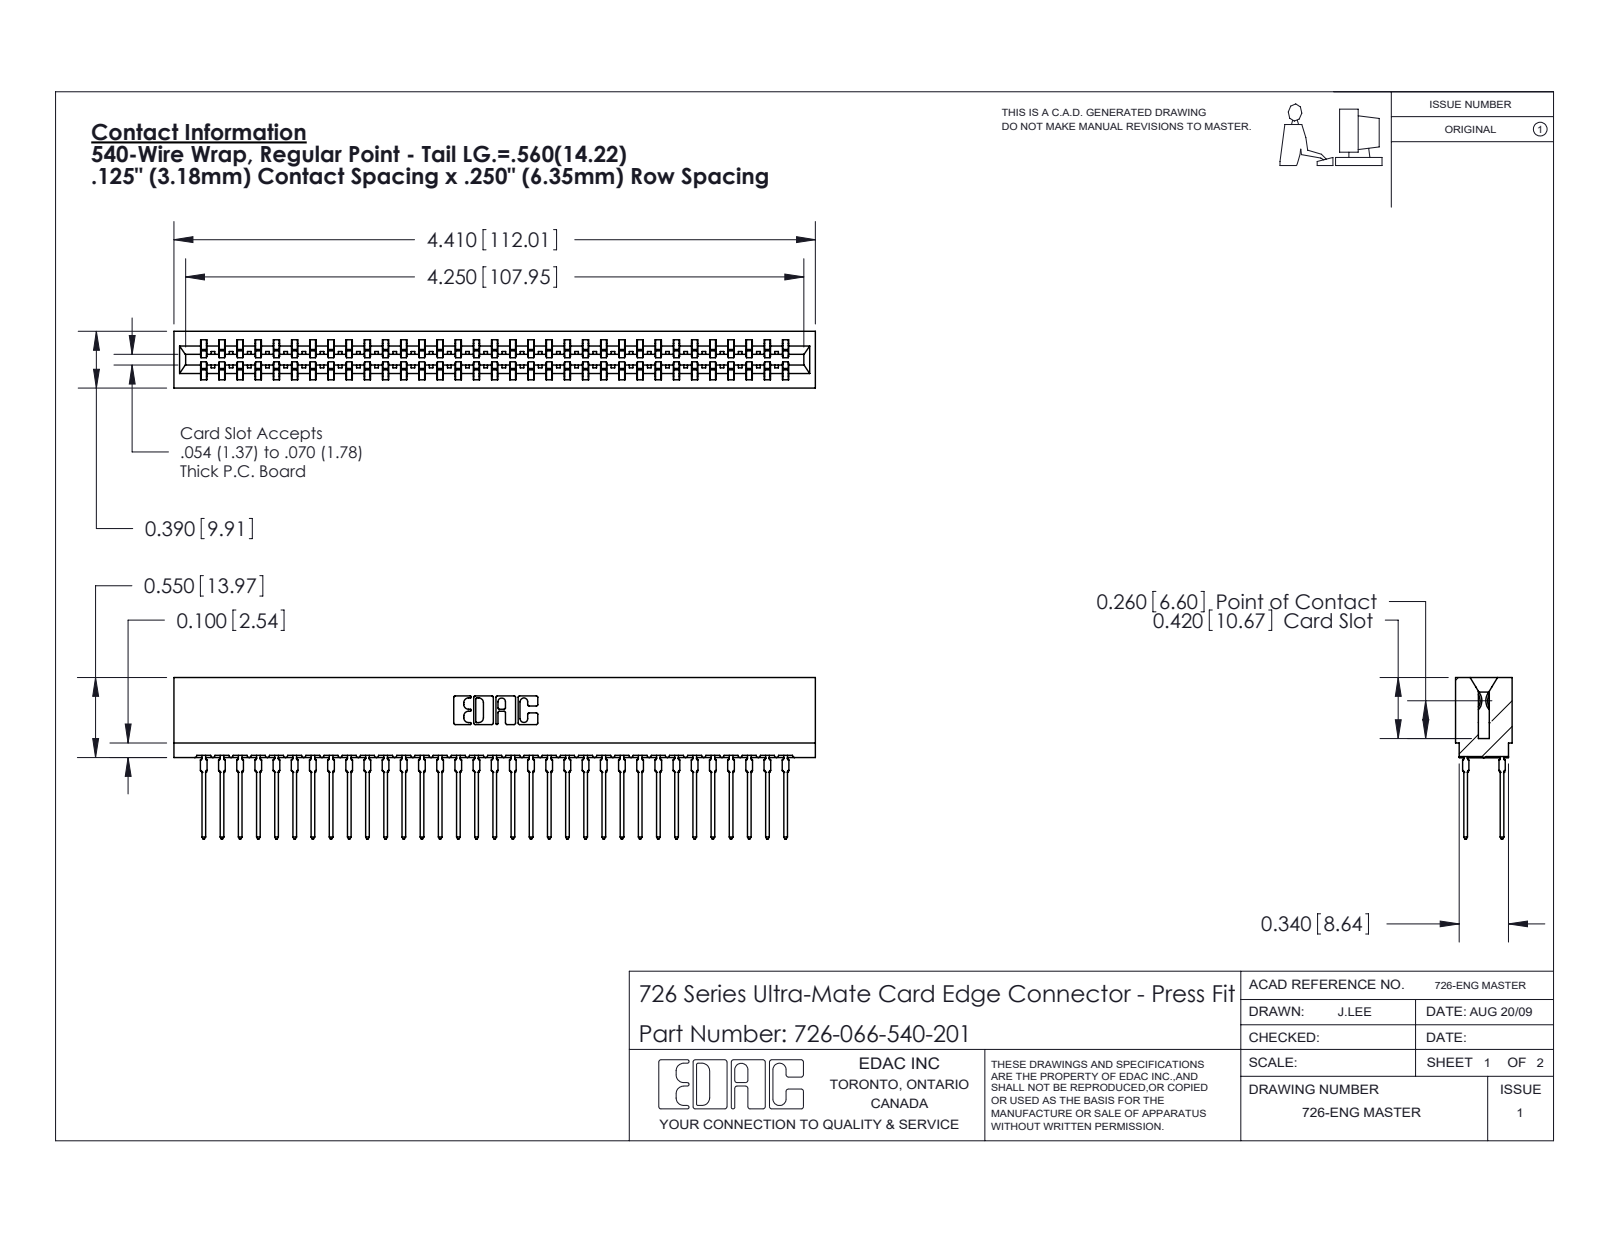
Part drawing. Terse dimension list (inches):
name: 726-066-540-201; 726 Part_.515 Slot Depth - 01; 746-292-001_540
written by: SolidWorks 2020 (CONFIG_CONTROL_DESIGN)
unit: in
bodies: 67 solids, 6004 faces (3091 planar, 1197 cylindrical, 1716 other)
size: 4.41 × 1.109 × 0.39
volume: 0.644 in³; area: 28.46 in²
rounds: 132× R0.021, 34× R0.015, 22× R0.01, 8× R0.005, 8× R0.011, 6× R0.007, 6× R0.031, 3× R0.026
face distances: 0.057, 0.333, 0.25, 0.025, 0.307, 0.39, 0.083, 0.275, 0.5, 0.75
